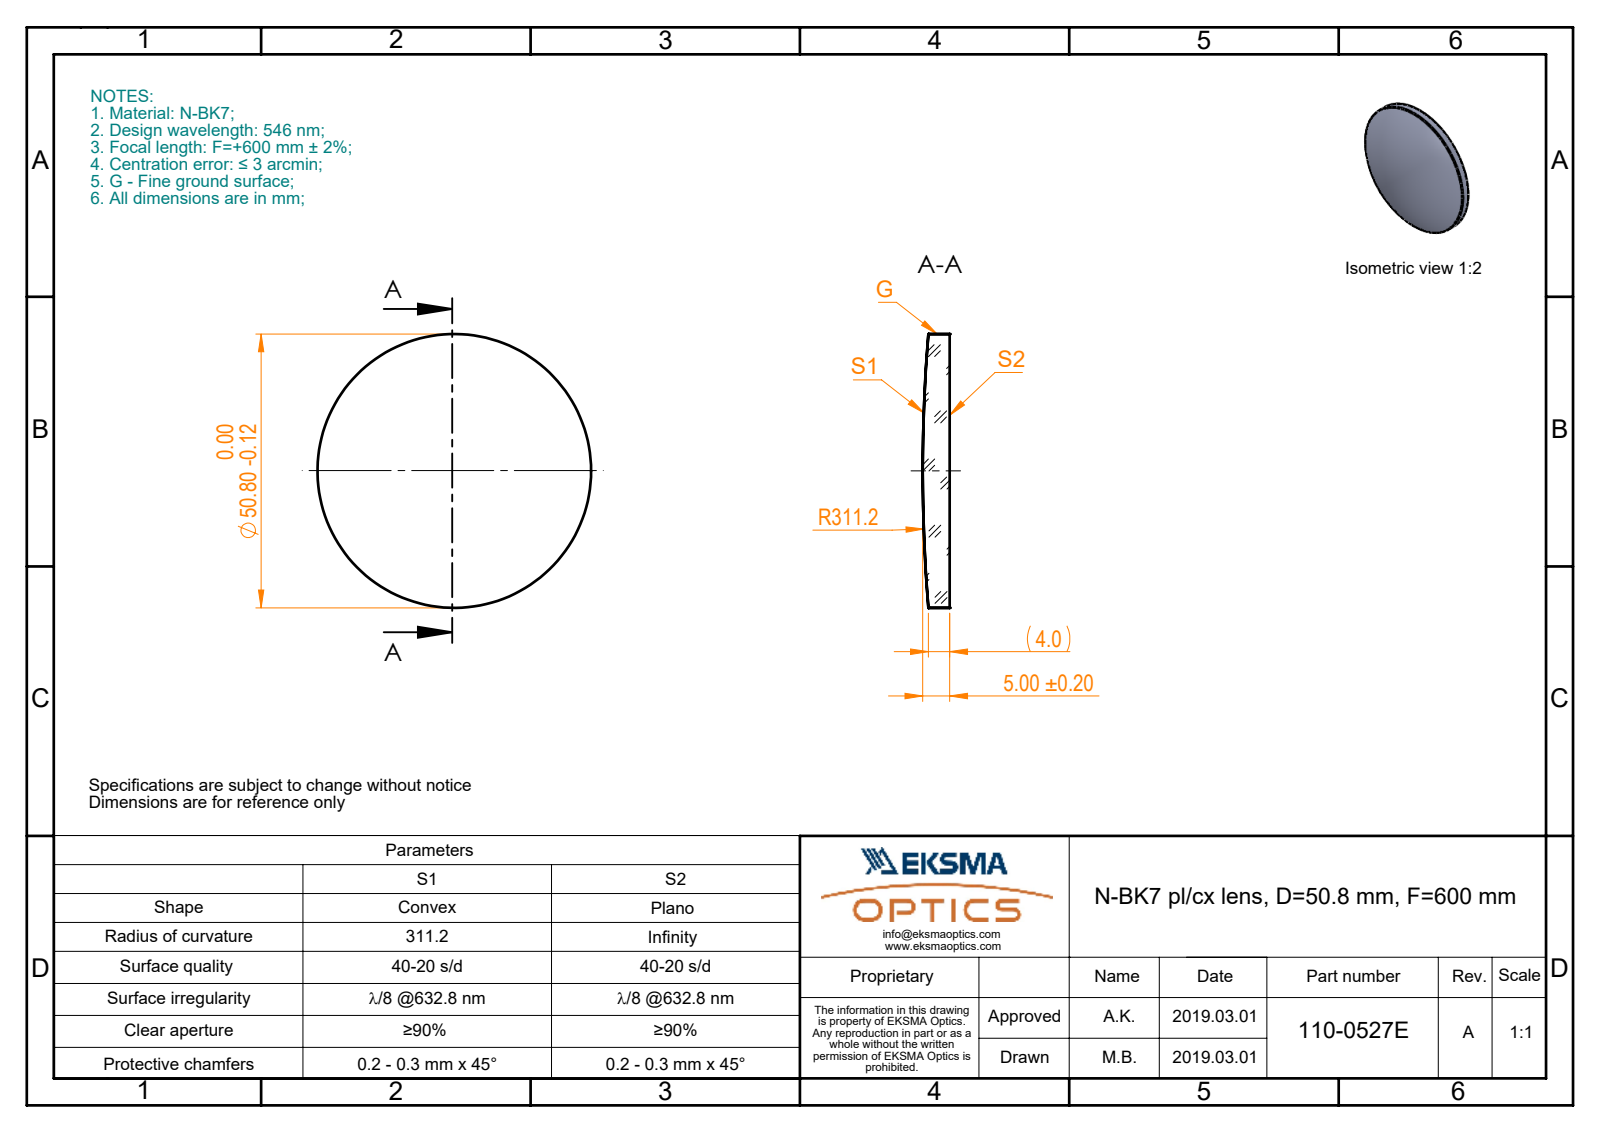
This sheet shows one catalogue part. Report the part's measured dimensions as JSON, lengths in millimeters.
{"part_name": "110-0527E BK7 pl-cx 50.8 F600", "step_written_by": "SolidWorks 2017 (CONFIG_CONTROL_DESIGN)", "units": "millimeters", "bodies": {"solids": 1, "faces": 5, "planar": 1, "cylindrical": 2, "other": 2}, "overall_size": [50.8, 50.8, 5], "volume_mm3": 9083, "surface_area_mm2": 4689, "round_bosses_or_shafts": [[50.8, 1]]}
